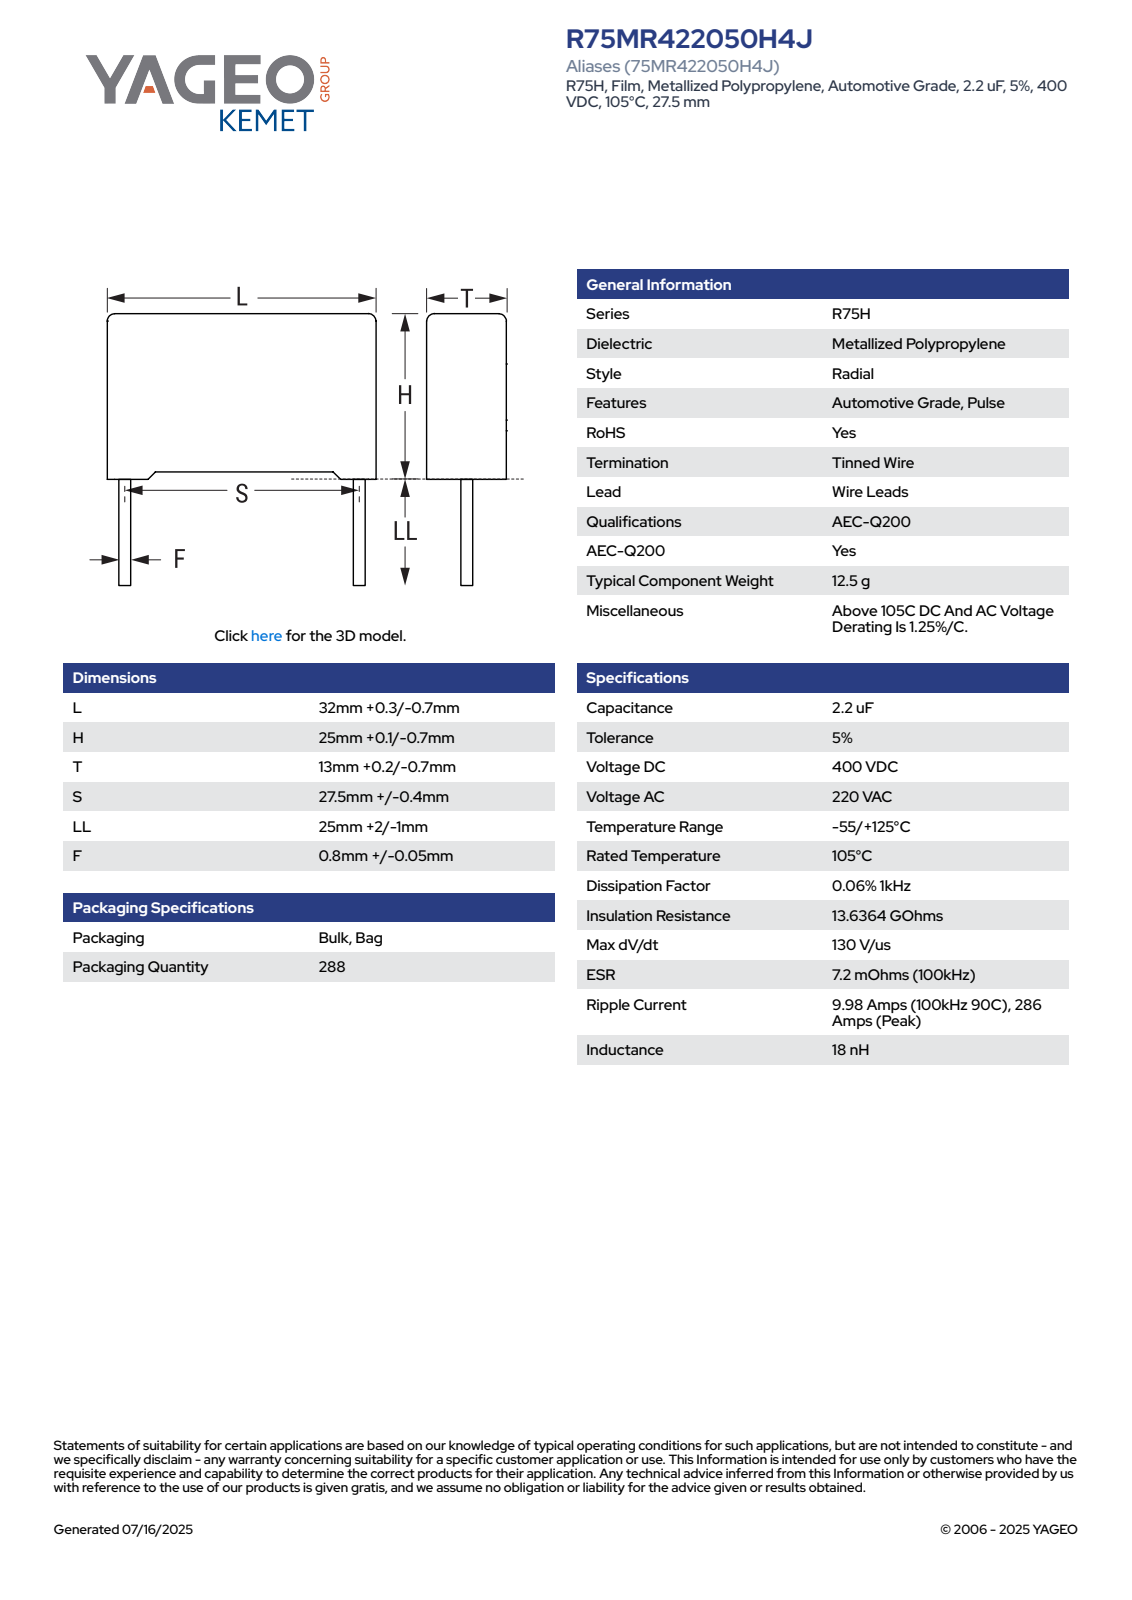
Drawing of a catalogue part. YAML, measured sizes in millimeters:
part_name: "CFR_RB2_32X25X13_L32.3H25.1T13.2S27.5LL27F0.85"
step_written_by: "SolidWorks 2021 (AUTOMOTIVE_DESIGN)"
units: millimeters
bodies: {solids: 4, faces: 85, planar: 77, cylindrical: 8, other: 0}
overall_size: [52.1, 32.3, 13.21]
volume: 10406
surface_area: 3331
round_bosses_or_shafts:
  - {diameter: 0.85, count: 2}
partial_cylinders:
  - {radius: 0.5, count: 4}
face_to_face_distances: [13.2, 32.3, 24.23, 24.35, 0.75, 0.87, 25.1, 1.08, 13.21, 31.22]
